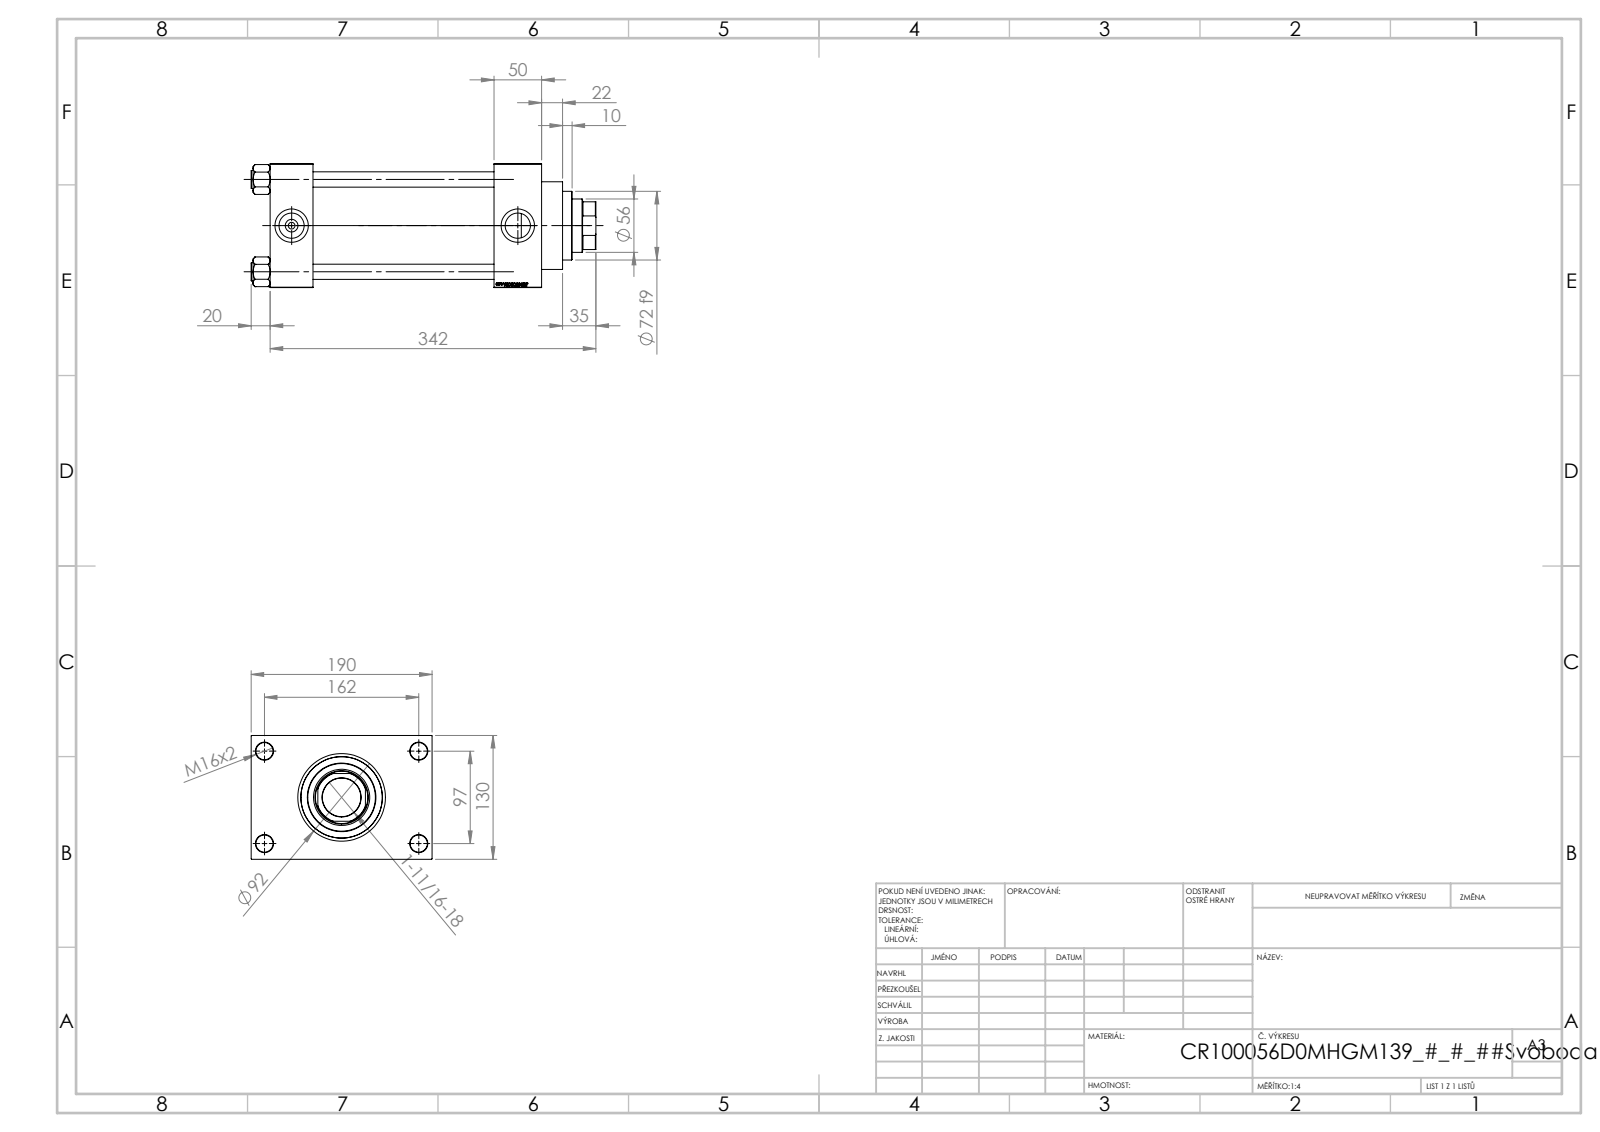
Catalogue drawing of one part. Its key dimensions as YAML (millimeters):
part_name: "V215CR_D_TYCINKA; V215CR_D_Body; V215_VC_A; V215CR_VCP_D (+1 more)"
step_written_by: "SolidWorks 2019 (CONFIG_CONTROL_DESIGN)"
units: millimeters
bodies: {solids: 11, faces: 1151, planar: 545, cylindrical: 88, other: 518}
overall_size: [362, 190, 130]
volume: 3132000
surface_area: 484238
round_holes:
  - {diameter: 16, count: 4}
  - {diameter: 18, count: 4}
  - {diameter: 7, count: 2}
  - {diameter: 26.44, count: 2}
  - {diameter: 35, count: 2}
  - {diameter: 40.5, count: 1}
  - {diameter: 56, count: 1}
  - {diameter: 59, count: 1}
  - {diameter: 76, count: 1}
  - {diameter: 85.5, count: 1}
  - {diameter: 100, count: 1}
round_bosses_or_shafts:
  - {diameter: 19, count: 4}
  - {diameter: 106, count: 1}
  - {diameter: 92, count: 1}
  - {diameter: 72, count: 1}
partial_cylinders:
  - {radius: 27, count: 1}
face_to_face_distances: [190, 130, 50, 45, 235, 285, 240, 30, 160, 96]
hole_center_spacings: [32.55, 68.52, 94.41, 96.9, 102.27, 129.45, 161.73, 97]
